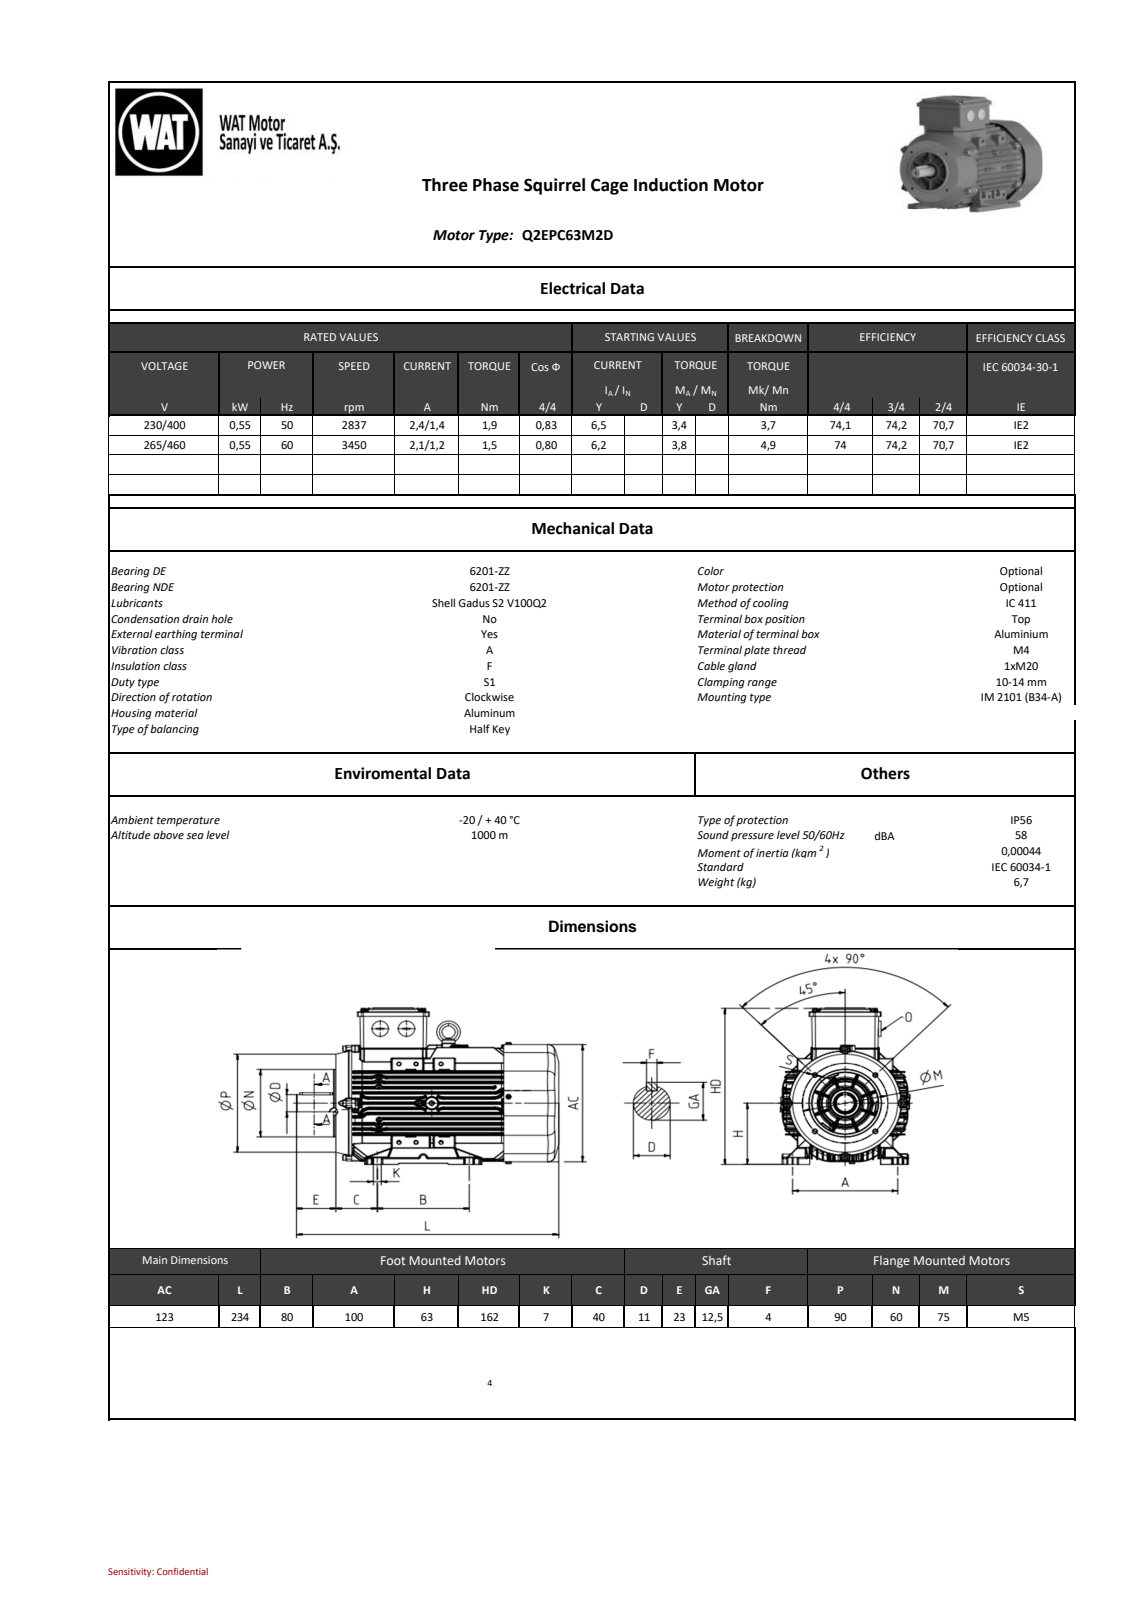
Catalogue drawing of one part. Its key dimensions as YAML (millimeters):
part_name: "QE Series_ 63_B34a_Deep Cover__stp_objects"
step_written_by: "SIEMENS PLM Software NX2206.8101 (AP203_CONFIGURATION_CONTROLLED_3D_DESIGN_OF_MECHANICAL_PARTS_AND_ASSEMBLIES_MIM_LF)"
units: millimeters
bodies: {solids: 0, faces: 1425, planar: 826, cylindrical: 438, other: 161}
overall_size: [233.47, 162.1, 126.28]
round_holes:
  - {diameter: 2.5, count: 4}
  - {diameter: 3.3, count: 4}
  - {diameter: 3.65, count: 4}
  - {diameter: 3.8, count: 4}
  - {diameter: 4.2, count: 4}
  - {diameter: 3, count: 3}
  - {diameter: 7, count: 2}
  - {diameter: 5, count: 1}
  - {diameter: 8, count: 1}
  - {diameter: 14.96, count: 1}
  - {diameter: 19, count: 1}
  - {diameter: 19.84, count: 1}
round_bosses_or_shafts:
  - {diameter: 8, count: 8}
  - {diameter: 4.8, count: 4}
  - {diameter: 123, count: 1}
  - {diameter: 121, count: 1}
  - {diameter: 61, count: 1}
  - {diameter: 60, count: 1}
  - {diameter: 25.28, count: 1}
  - {diameter: 11, count: 1}
partial_cylinders:
  - {radius: 0.5, count: 110}
  - {radius: 1, count: 102}
  - {radius: 1.5, count: 16}
  - {radius: 4, count: 12}
  - {radius: 2, count: 8}
  - {radius: 0.1, count: 7}
  - {radius: 8, count: 6}
  - {radius: 0.3, count: 5}
face_to_face_distances: [5, 7.02, 27.96, 28.05, 10.5, 6.93, 13.81, 6.88, 21.03, 14.16]
hole_center_spacings: [37.5, 54, 10, 75, 5, 16.98, 31.5, 31.52]
